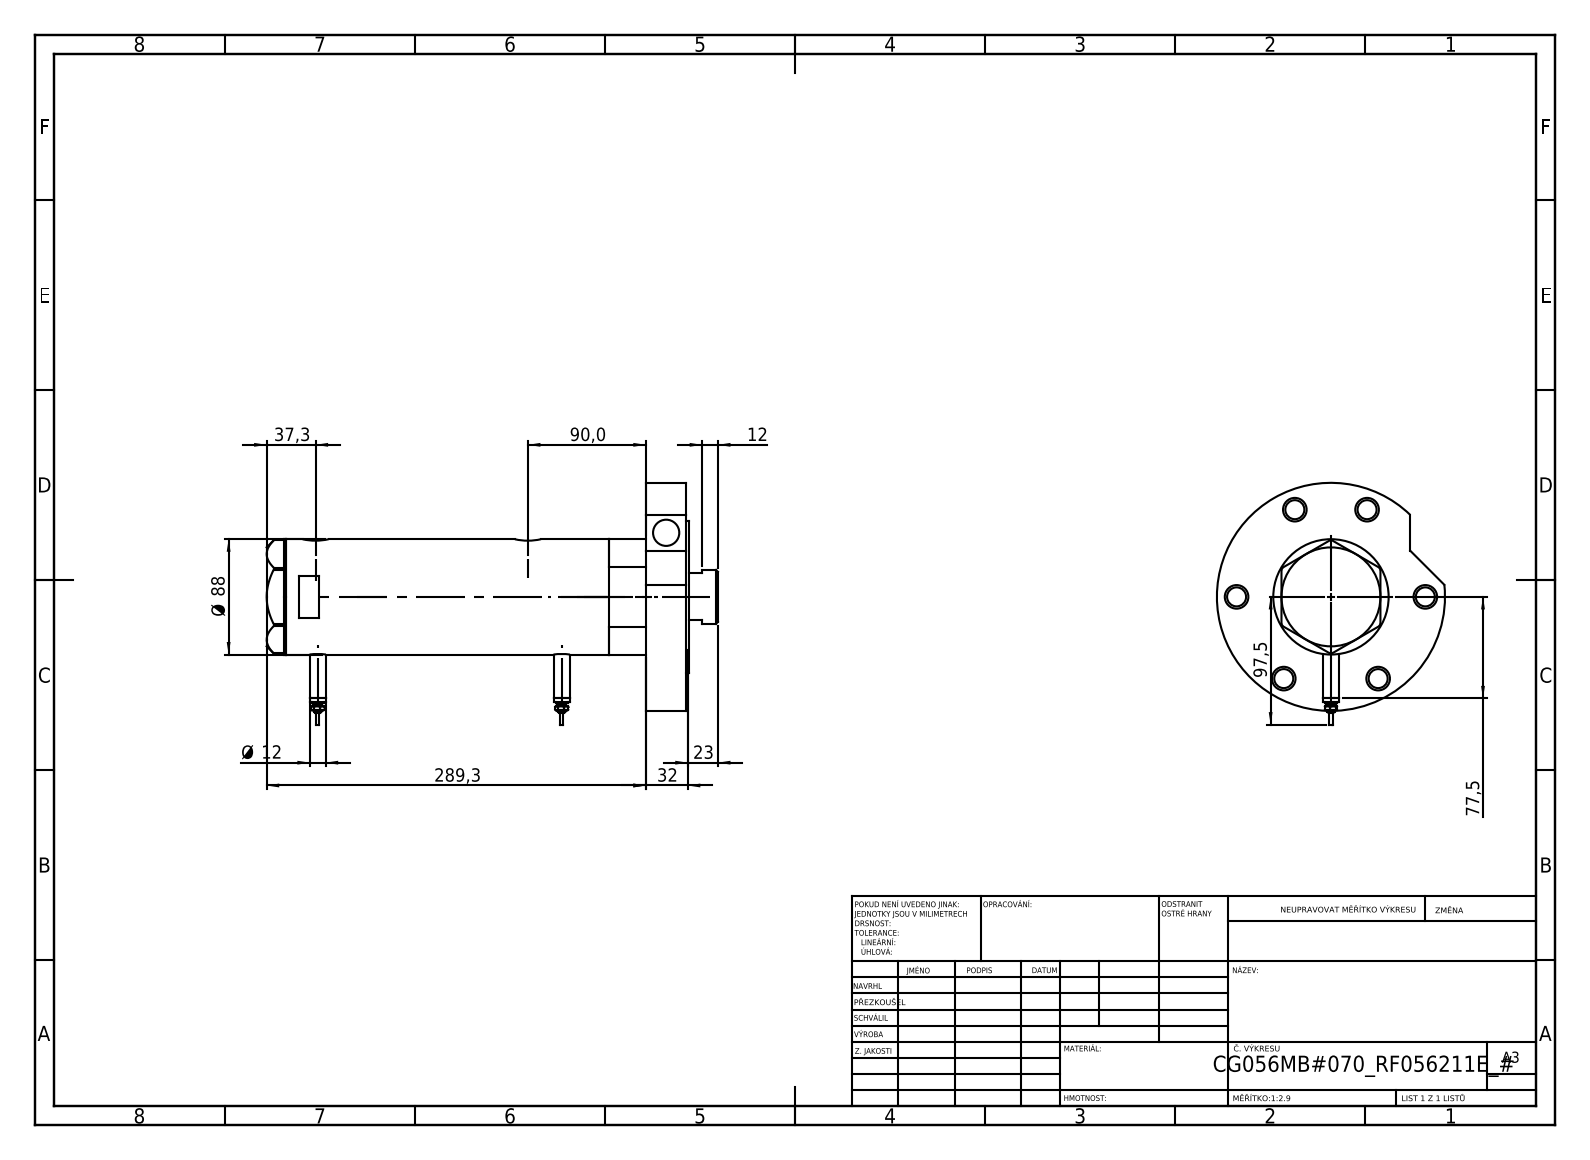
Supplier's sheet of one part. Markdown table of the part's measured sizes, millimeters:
| quantity | value |
| --- | --- |
| part name | V270CG_BACK; V270CG_FRONT; Switch; V270CG_RF211E (+2 more) |
| STEP written by | SolidWorks 2019 (CONFIG_CONTROL_DESIGN) |
| units | millimeters |
| bodies | 7 solids, 257 faces (91 planar, 102 cylindrical, 64 other) |
| overall size | 344.3 × 184.5 × 174 |
| volume | 2 343 000 mm³ |
| surface area | 332 794 mm² |
| round holes (diameter × count) | 14.5 × 7, 18 × 6, 20 × 3, 12.5 × 2, 13.16 × 2, 42 × 1, 43.5 × 1, 56 × 1, 60 × 1, 75 × 1, 80 × 1 |
| round bosses / shafts (diameter × count) | 12 × 2, 9 × 2, 7 × 2, 4.5 × 2, 2.5 × 2, 174 × 1, 116 × 1, 88 × 1 |
| main face-to-face distances | 31, 2, 307.3, 274.3, 305.3, 33, 184.4, 89.9, 120.9, 122.9 |
| hole center spacings | 72, 80, 119.73, 124.71, 129.15, 143.69, 1.7, 25.8 |
